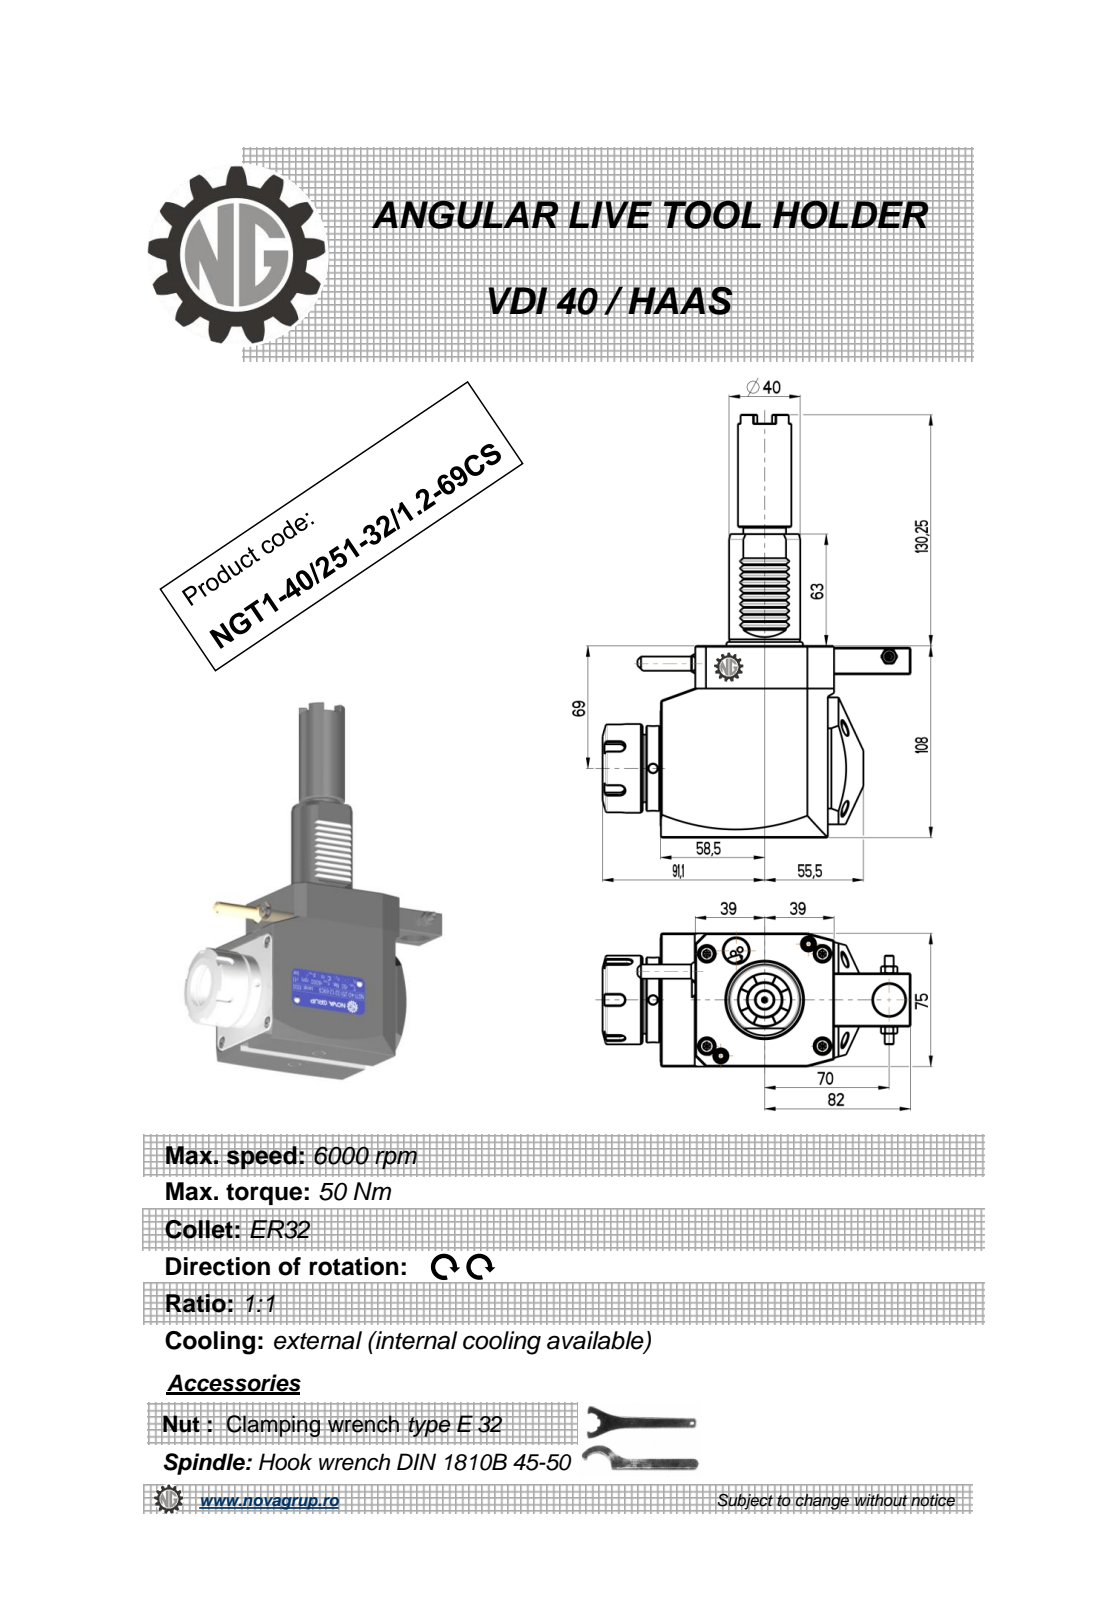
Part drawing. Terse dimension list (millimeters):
name: NGT1_40_251_32_1_2_69CS
written by: PRO/ENGINEER BY PARAMETRIC TECHNOLOGY CORPORATION, 2010280 (CONFIG_CONTROL_DESIGN)
unit: mm
bodies: 1 solid, 481 faces (240 planar, 98 cylindrical, 143 other)
size: 238.25 × 173.1 × 76.6
volume: 959 698 mm³; area: 81 374 mm²
holes: 3× ⌀5, 1× ⌀3, 1× ⌀4.2, 1× ⌀9.5, 1× ⌀18, 1× ⌀19.5, 1× ⌀27
bosses: 1× ⌀50, 1× ⌀48, 1× ⌀41.5, 1× ⌀41, 1× ⌀40, 1× ⌀30, 1× ⌀24, 1× ⌀10
rounds: 12× R0.26, 10× R0.3, 6× R0.2, 5× R3, 2× R5.8, 2× R6, 2× R600, 1× R0.5
face distances: 75, 108, 1, 22.5, 3.5, 19.5, 20, 97.5, 78, 19.3
hole spacings: 16.19, 61.13, 61.5, 62.75, 70, 132.75, 146.94
